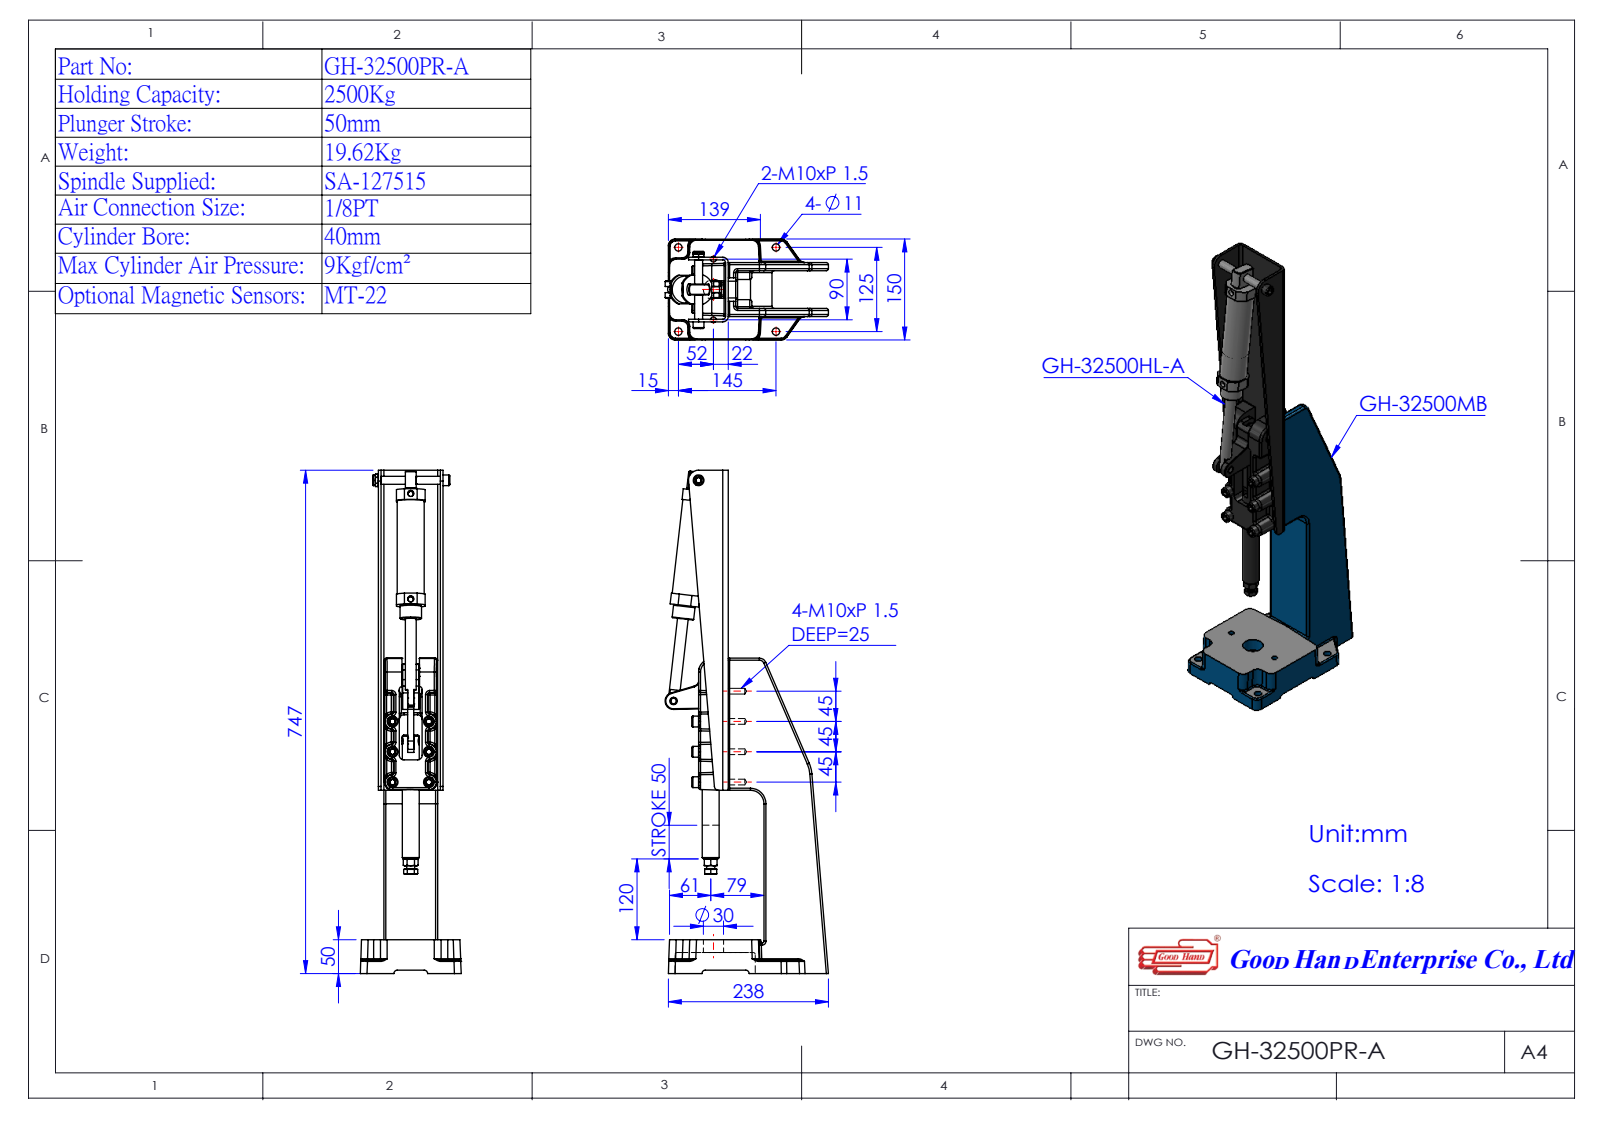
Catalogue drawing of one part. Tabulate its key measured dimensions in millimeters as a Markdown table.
| quantity | value |
| --- | --- |
| part name | Group4^GH-32500HL-A(簡化); Group3^GH-32500HL-A(簡化); Group1^GH-32500HL-A(簡化); SDA serial cylinder A_SDA 40×100-1^GH-32500HL-A(簡化) (+6 more) |
| STEP written by | SolidWorks 2016 (AUTOMOTIVE_DESIGN) |
| units | millimeters |
| bodies | 8 solids, 1602 faces (746 planar, 424 cylindrical, 432 other) |
| overall size | 747 × 243.25 × 149.79 |
| volume | 2 863 000 mm³ |
| surface area | 647 885 mm² |
| round holes (diameter × count) | 8.5 × 10, 11 × 4, 7 × 2, 7.9 × 2, 2.68 × 1, 9 × 1, 10.2 × 1, 12 × 1, 15 × 1, 16 × 1, 18 × 1, 25 × 1 |
| round bosses / shafts (diameter × count) | 16 × 8, 10 × 7, 40 × 1, 38 × 1, 32 × 1, 31 × 1, 18 × 1, 12 × 1 |
| partial cylindrical surfaces (radius × count) | 3 × 76, 10 × 24, 7 × 6, 12 × 6, 8 × 5, 5 × 4, 20 × 4, 12.5 × 3 |
| main face-to-face distances | 4, 12, 68, 88, 80, 16, 20, 56, 84, 92 |
| hole center spacings | 45, 70.29, 90, 54, 104.96, 45.18, 54.87, 78.81 |
